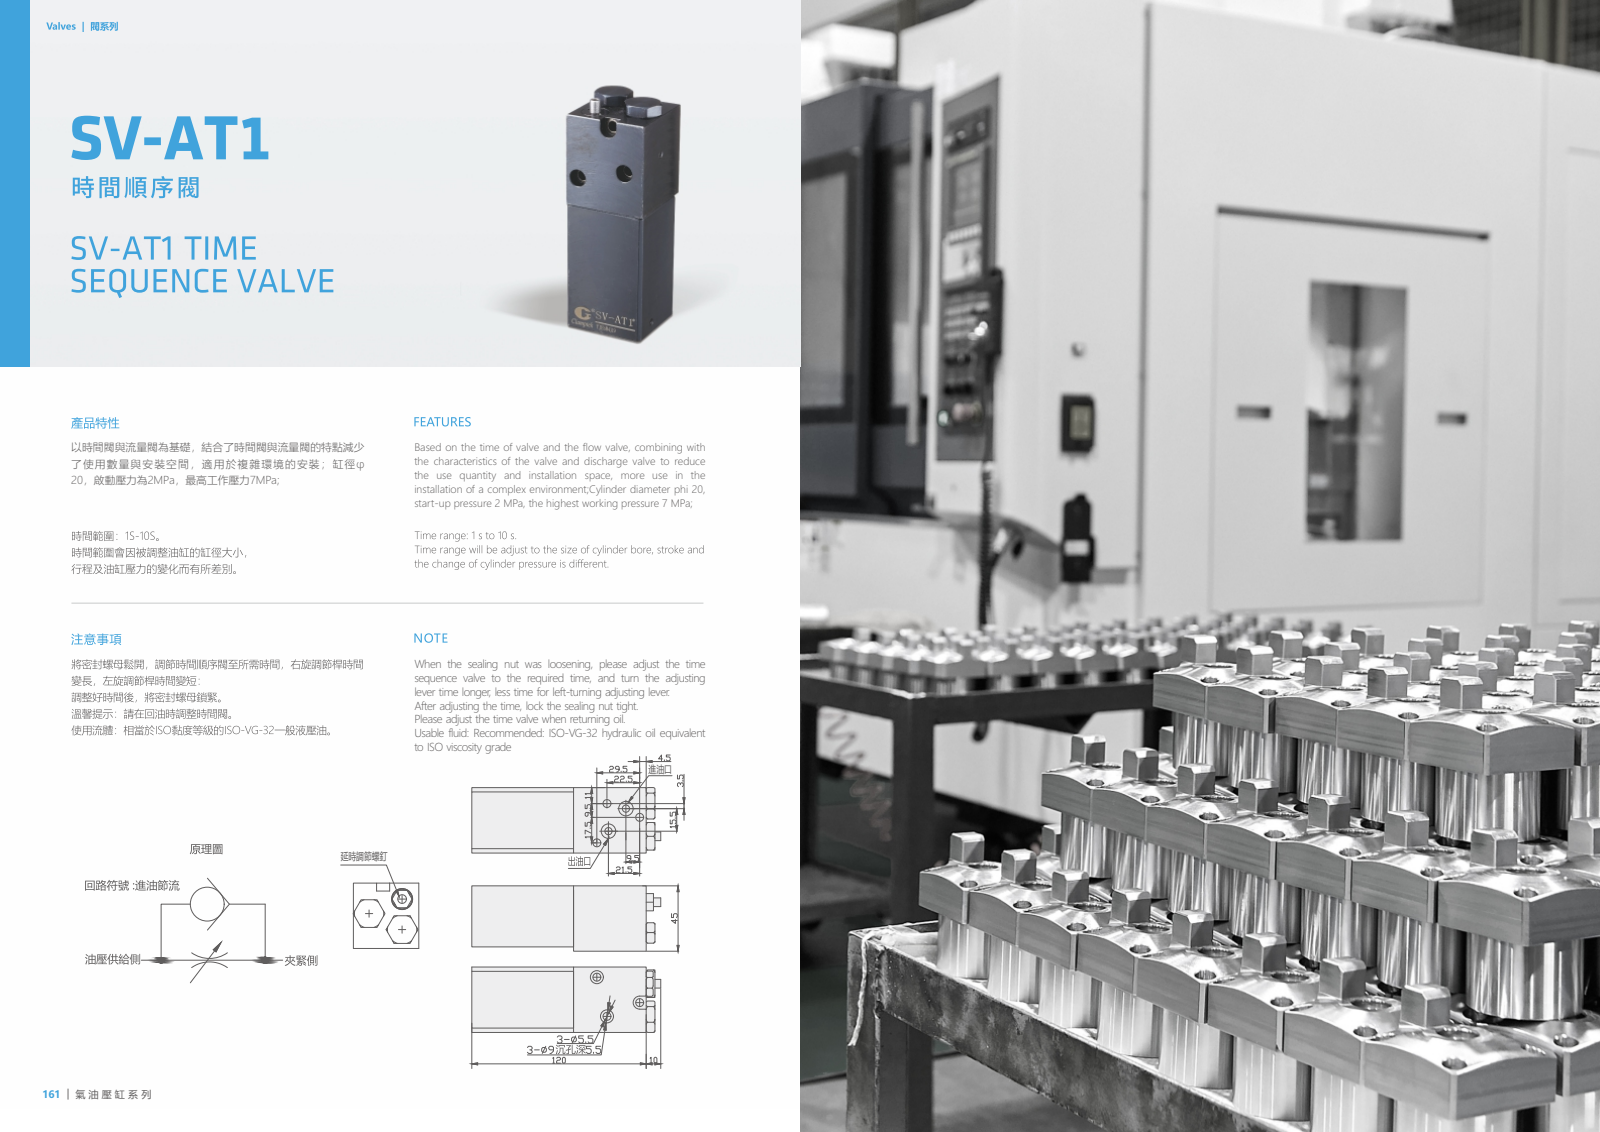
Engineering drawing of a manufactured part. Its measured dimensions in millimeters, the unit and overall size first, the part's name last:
Units: millimetres
Overall size (bounding box): 127 × 45.02 × 45
Round holes (diameter × count): ⌀3 ×8, ⌀5.5 ×8, ⌀10 ×6, ⌀5 ×5, ⌀1 ×4, ⌀4 ×4, ⌀4.2 ×4, ⌀6 ×4, ⌀0.5 ×3, ⌀10.5 ×3, ⌀2.5 ×2, ⌀6.5 ×2
Round bosses / shafts (diameter × count): ⌀10 ×3, ⌀12 ×2, ⌀10.8 ×2, ⌀7 ×2, ⌀30 ×1, ⌀25 ×1, ⌀21 ×1, ⌀20 ×1
Partial cylindrical surfaces — rounded edges, fillets, slot ends (radius × count): R4.5 ×1
Main face-to-face distances: 45, 42, 3, 50, 79.5, 40.5, 9.5, 120, 70, 5.5
Hole centre spacings: 22.3, 9.65, 10.01, 12.5, 15.75, 30, 31.94, 33
Volume: 195 307 mm³ · Surface area: 74 877 mm²
Bodies: 15 solids, 516 faces (153 planar, 275 cylindrical, 88 other)
Part name (STEP PRODUCT): ПъЦб
STEP written by: SolidWorks 2017 (CONFIG_CONTROL_DESIGN)
